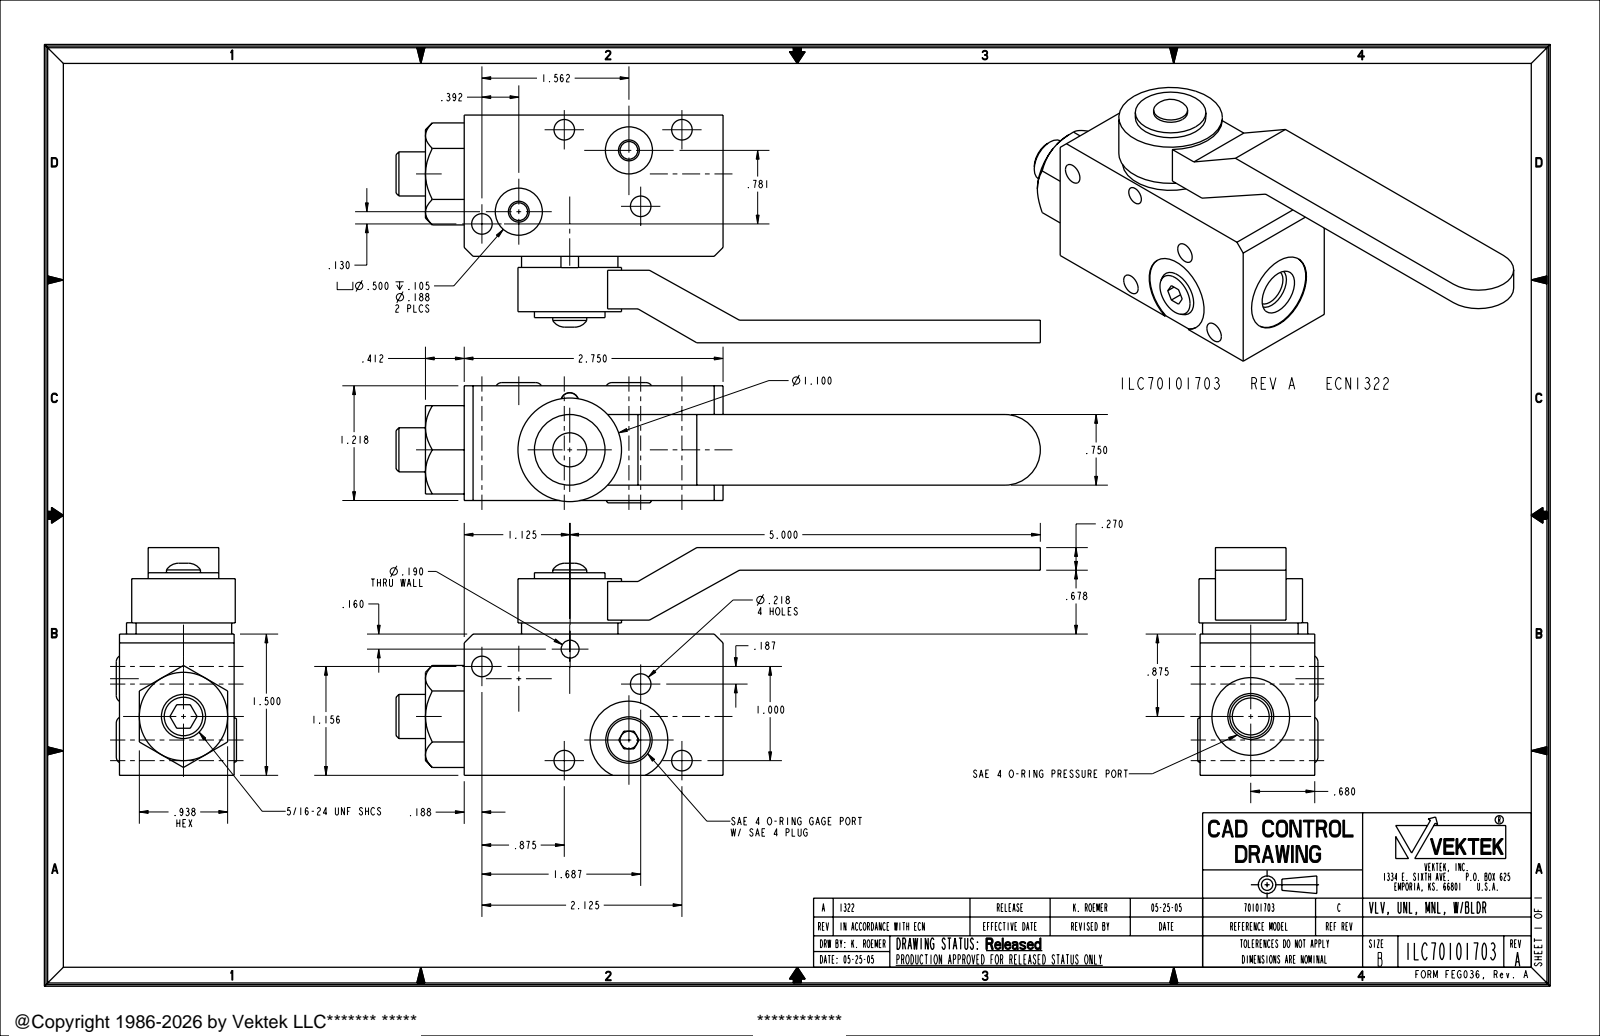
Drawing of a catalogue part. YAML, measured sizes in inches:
part_name: "ILC70101703"
step_written_by: "PRO/ENGINEER BY PARAMETRIC TECHNOLOGY CORPORATION, 2004290 (AUTOMOTIVE_DESIGN_CC2)"
units: inches
bodies: {solids: 3, faces: 150, planar: 62, cylindrical: 50, other: 38}
overall_size: [6.845, 2.418, 1.277]
volume: 6.386
surface_area: 41.73
round_holes:
  - {diameter: 0.218, count: 4}
  - {diameter: 0.188, count: 2}
  - {diameter: 0.19, count: 2}
  - {diameter: 0.392, count: 2}
  - {diameter: 0.5, count: 2}
  - {diameter: 0.825, count: 2}
  - {diameter: 0.694, count: 1}
round_bosses_or_shafts:
  - {diameter: 1.1, count: 1}
  - {diameter: 1.024, count: 1}
  - {diameter: 0.75, count: 1}
  - {diameter: 0.469, count: 1}
  - {diameter: 0.437, count: 1}
  - {diameter: 0.377, count: 1}
  - {diameter: 0.361, count: 1}
  - {diameter: 0.187, count: 1}
partial_cylinders:
  - {radius: 0.375, count: 1}
face_to_face_distances: [1.218, 2.418, 1.5, 0.918, 2.178, 0.678, 0.24, 0.75, 0.305, 0.913]
hole_center_spacings: [0.413, 0.512, 0.604, 0.607, 0.629, 0.721, 0.837, 0.924]
